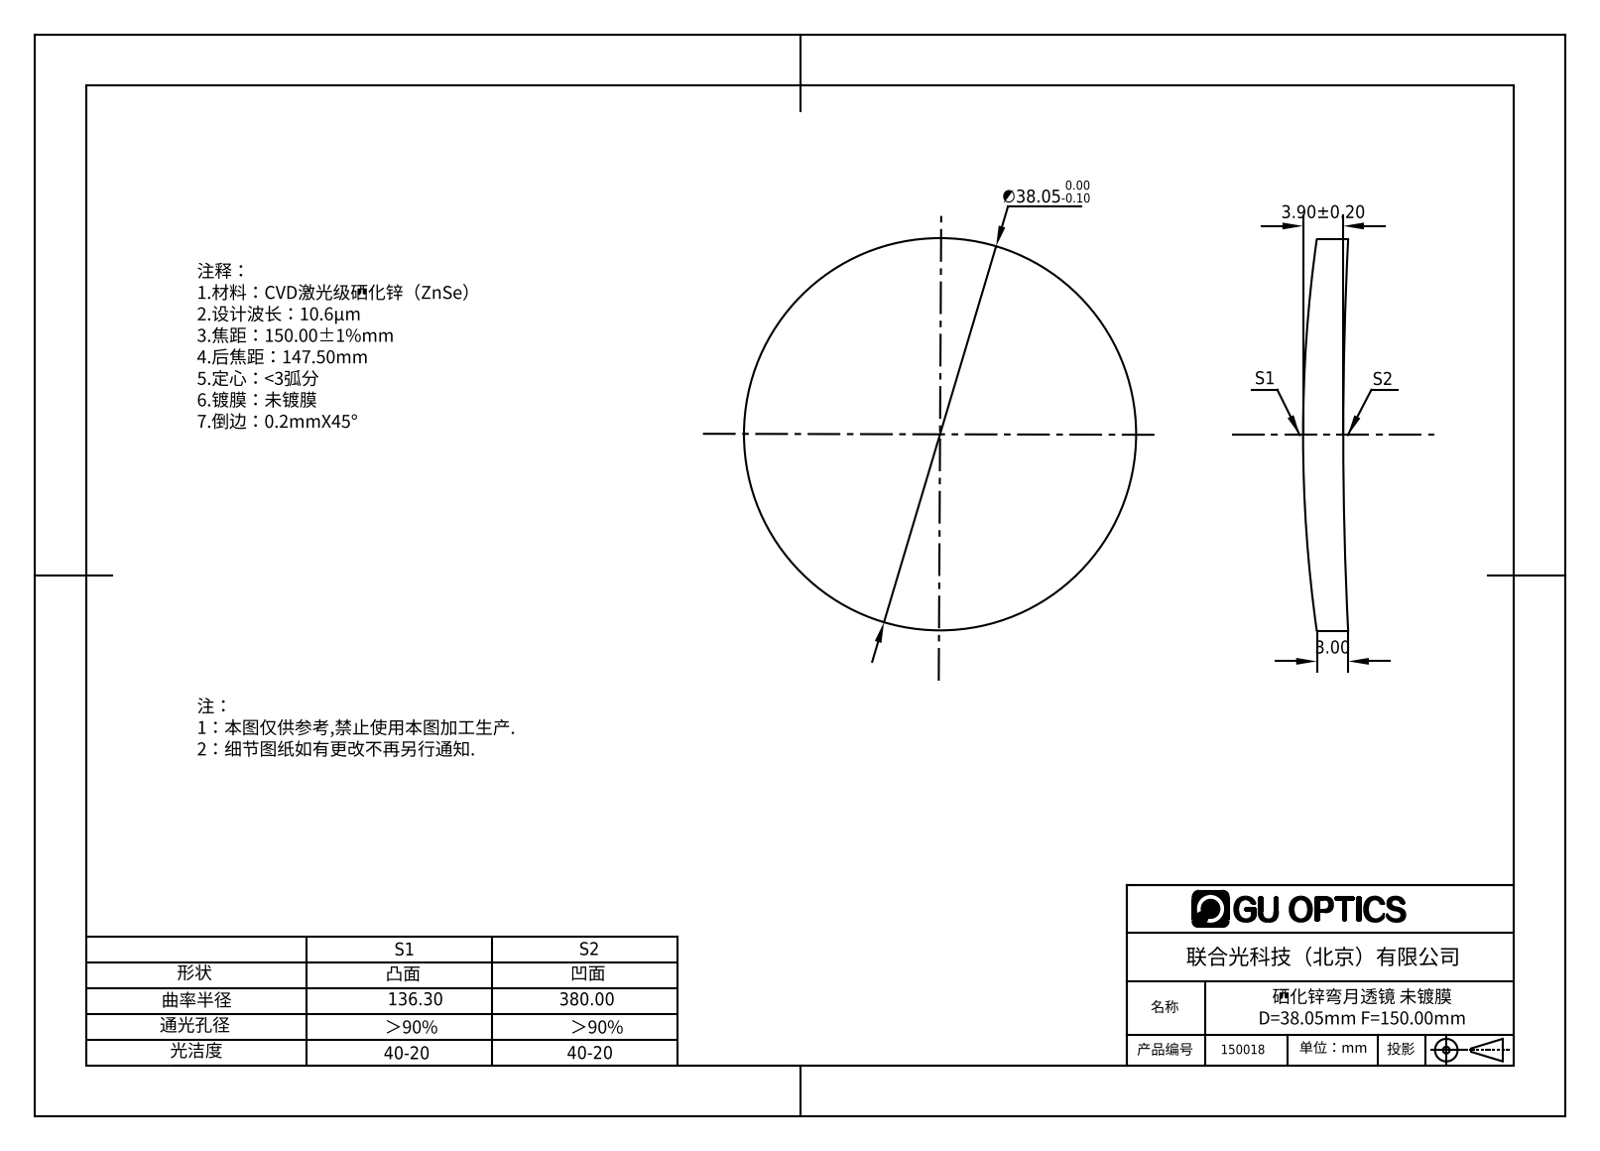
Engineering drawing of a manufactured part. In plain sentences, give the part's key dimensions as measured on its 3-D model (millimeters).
The part is named "150018". Its 3-D file was written by "SolidWorks 2016 (AUTOMOTIVE_DESIGN)". It is 1 solid with 6 faces: 0 planar, 2 cylindrical and 4 other. Overall it measures 38.05 by 38.05 by 4.38 millimeters. Its volume is 3 948 cubic millimeters and its surface area 2 644 square millimeters. Round bosses or shafts: 1 of diameter 38.05.
